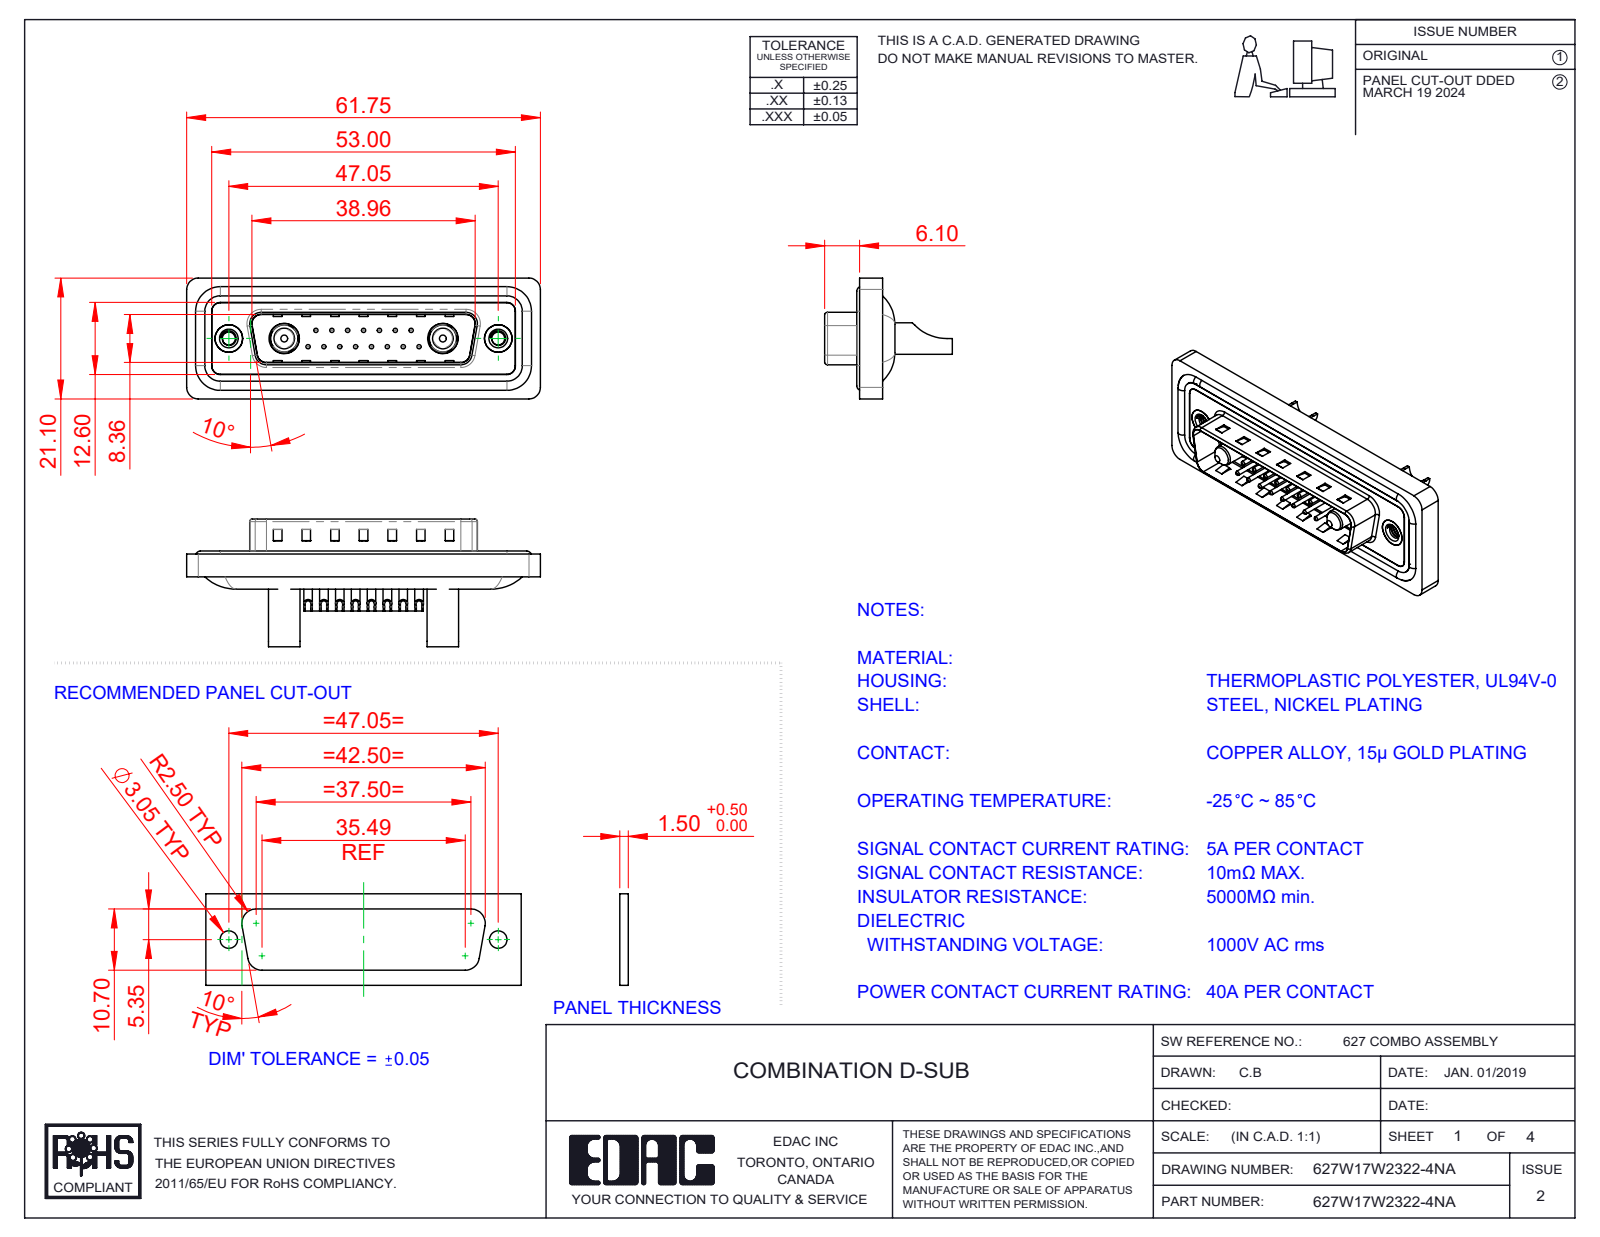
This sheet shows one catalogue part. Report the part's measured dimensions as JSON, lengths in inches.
{"part_name": "627Combo Contact Row 1_22; 627W17W2322-4NA; 627Combo Shell Rear_25 Contacts; 627Combo Housing_17W2 (+5 more)", "step_written_by": "SolidWorks 2023 (CONFIG_CONTROL_DESIGN)", "units": "inches", "bodies": {"solids": 26, "faces": 1122, "planar": 368, "cylindrical": 470, "other": 284}, "overall_size": [2.431, 0.878, 0.831], "volume_in3": 0.45, "surface_area_in2": 19.08, "round_holes": [[0.03, 15], [0.039, 15], [0.063, 15], [0.079, 15], [0.089, 2], [0.157, 2], [0.181, 2], [0.189, 2], [0.191, 2], [0.197, 2], [0.209, 2]], "round_bosses_or_shafts": [[0.059, 15], [0.063, 4], [0.217, 2], [0.205, 2], [0.193, 2], [0.187, 2], [0.148, 2], [0.142, 2]], "partial_cylinders_radius": [[0.059, 22], [0.079, 18], [0.02, 8], [0.063, 8], [0.039, 6], [0.01, 4], [0.024, 4], [0.026, 4]], "face_to_face_distances": [0.016, 0.059, 0.043, 0.063, 0.02, 0.122, 0.114, 0.032, 0.377, 0.161], "hole_center_spacings": [0.124, 0.109, 0.218, 0.327, 0.198, 0.295, 0.436, 0.198]}
